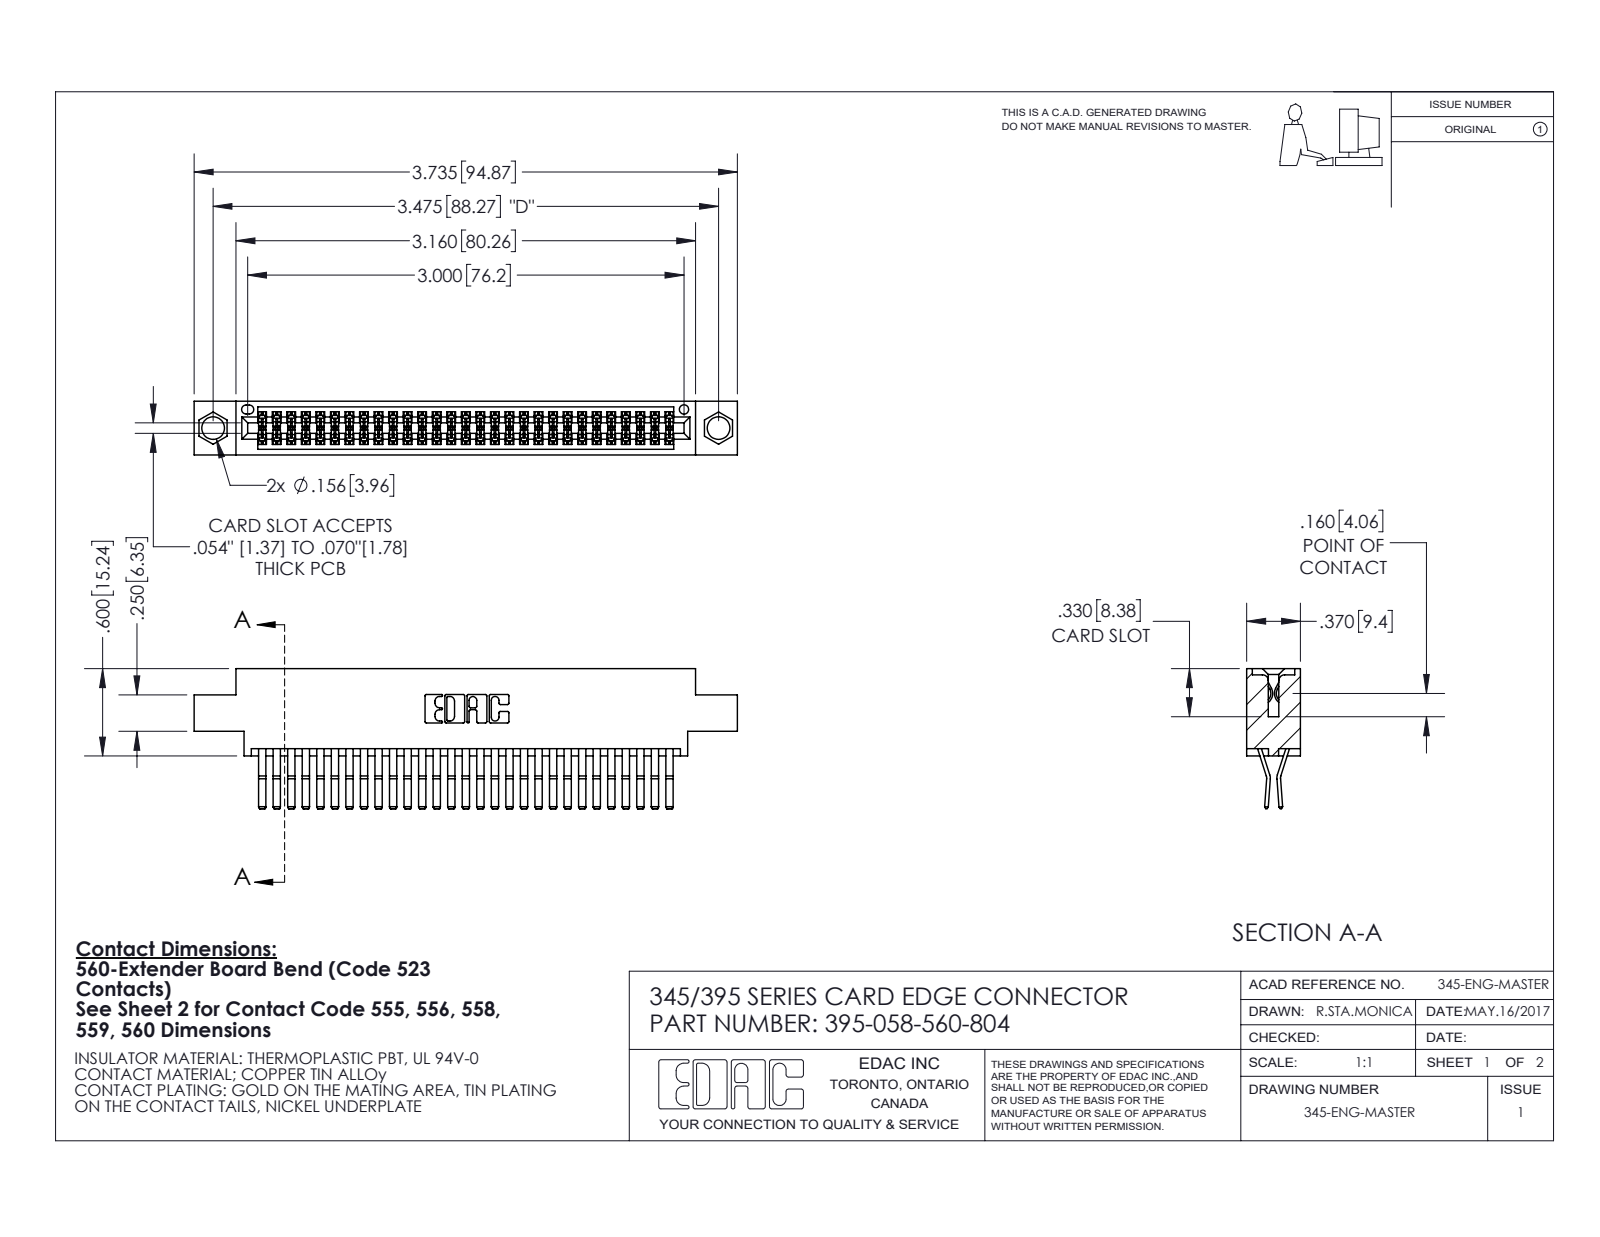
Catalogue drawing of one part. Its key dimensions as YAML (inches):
part_name: "345 Part_0.170 Offset - 0.156 Dia-TI; 395-058-560-804; 345-292-001_560 Tail"
step_written_by: "SolidWorks 2020 (CONFIG_CONTROL_DESIGN)"
units: inches
bodies: {solids: 59, faces: 3160, planar: 2012, cylindrical: 1148, other: 0}
overall_size: [3.735, 0.962, 0.37]
volume: 0.565
surface_area: 22.32
round_holes:
  - {diameter: 0.156, count: 2}
  - {diameter: 0.064, count: 1}
partial_cylinders:
  - {radius: 0.006, count: 87}
  - {radius: 0.01, count: 22}
  - {radius: 0.007, count: 6}
  - {radius: 0.031, count: 6}
  - {radius: 0.026, count: 3}
  - {radius: 0.01, count: 2}
  - {radius: 0.014, count: 2}
  - {radius: 0.019, count: 2}
face_to_face_distances: [0.025, 0.298, 0.072, 0.37, 0.2, 0.098, 0.272, 0.225, 0.175, 0.149]
hole_center_spacings: [0.27, 3.24, 3.475]
